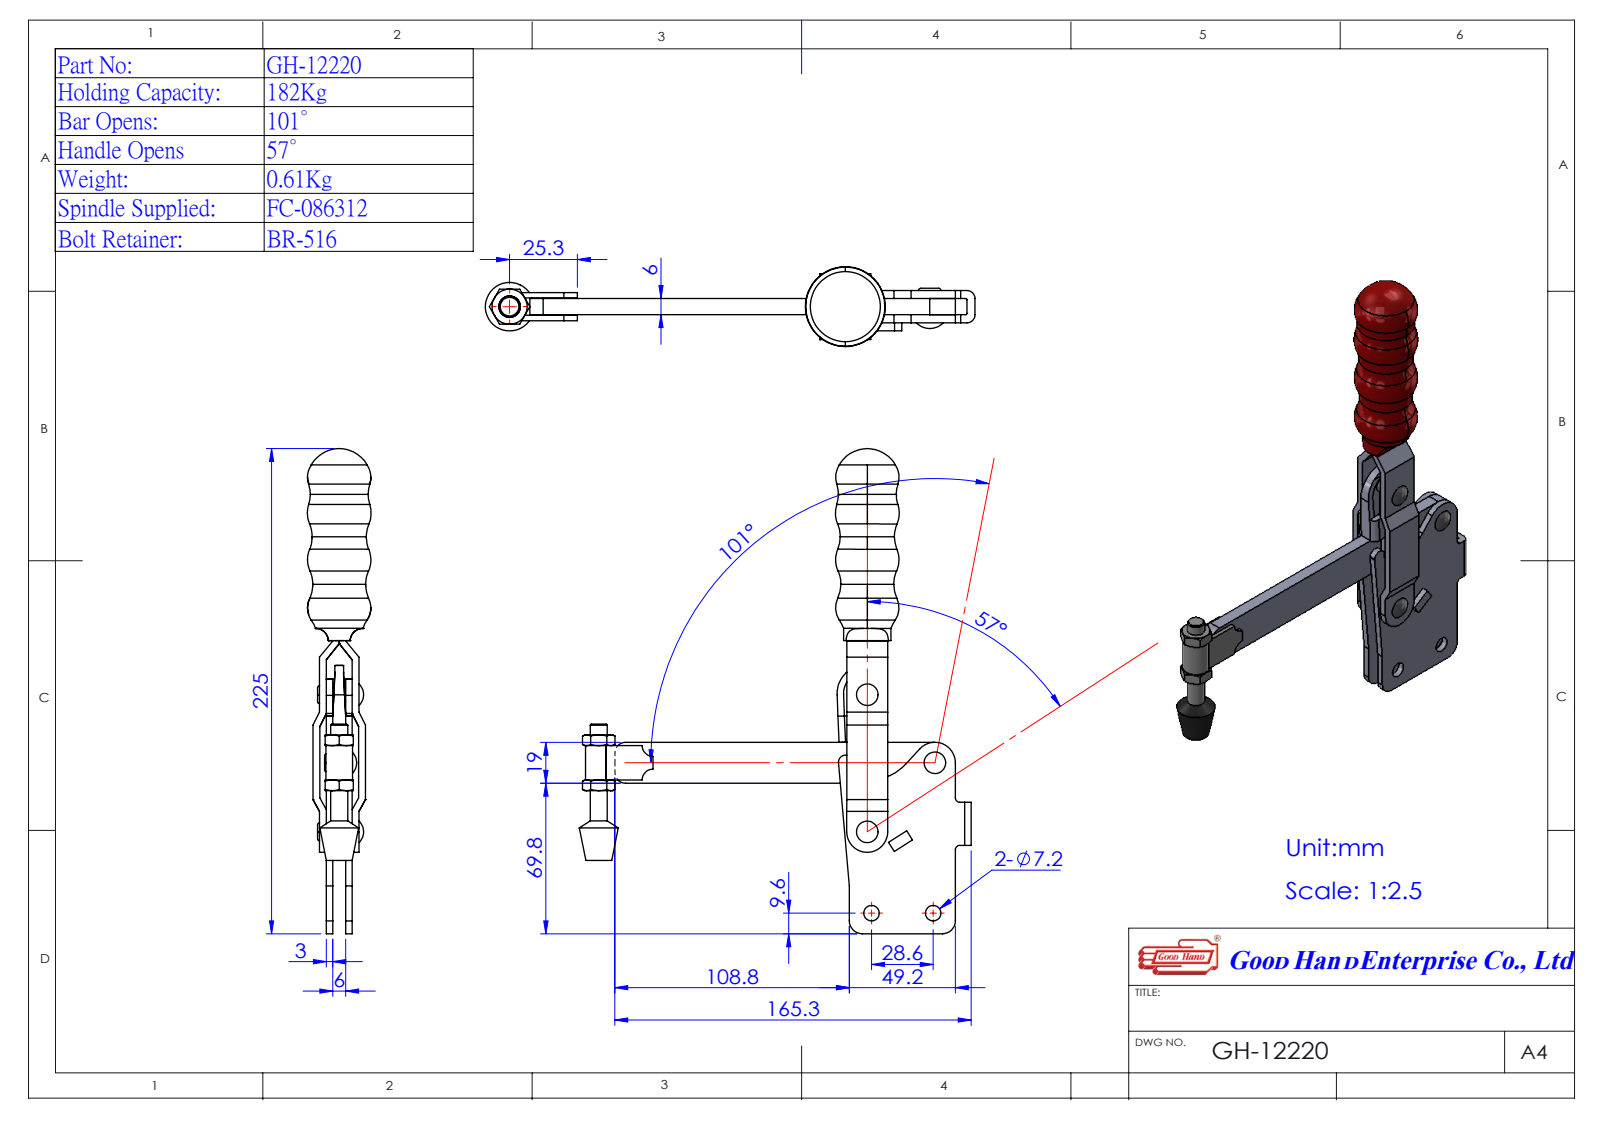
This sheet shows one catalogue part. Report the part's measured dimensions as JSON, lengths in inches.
{"part_name": "Group2^GH-12220(簡化); Group4^GH-12210(簡化)-1; Group1^GH-12220(簡化); 11221509-1^GH-12220(簡化) (+2 more)", "step_written_by": "SolidWorks 2016 (AUTOMOTIVE_DESIGN)", "units": "inches", "bodies": {"solids": 5, "faces": 276, "planar": 117, "cylindrical": 89, "other": 70}, "overall_size": [8.858, 7.463, 1.168], "volume_in3": 7.149, "surface_area_in2": 81.77, "round_holes": [[0.189, 4], [0.283, 2]], "round_bosses_or_shafts": [[0.866, 1], [0.312, 1]], "partial_cylinders_radius": [[0.118, 4], [0.236, 4], [0.02, 2], [0.079, 2], [0.099, 2], [0.285, 2], [0.374, 2], [0.039, 1]], "face_to_face_distances": [0.118, 0.354, 0.236, 0.472, 0.244, 0.598, 0.126, 0.717, 0.748, 0.48], "hole_center_spacings": [2.746, 1.126, 1.181, 1.244, 1.262, 1.487, 1.752, 1.765]}
